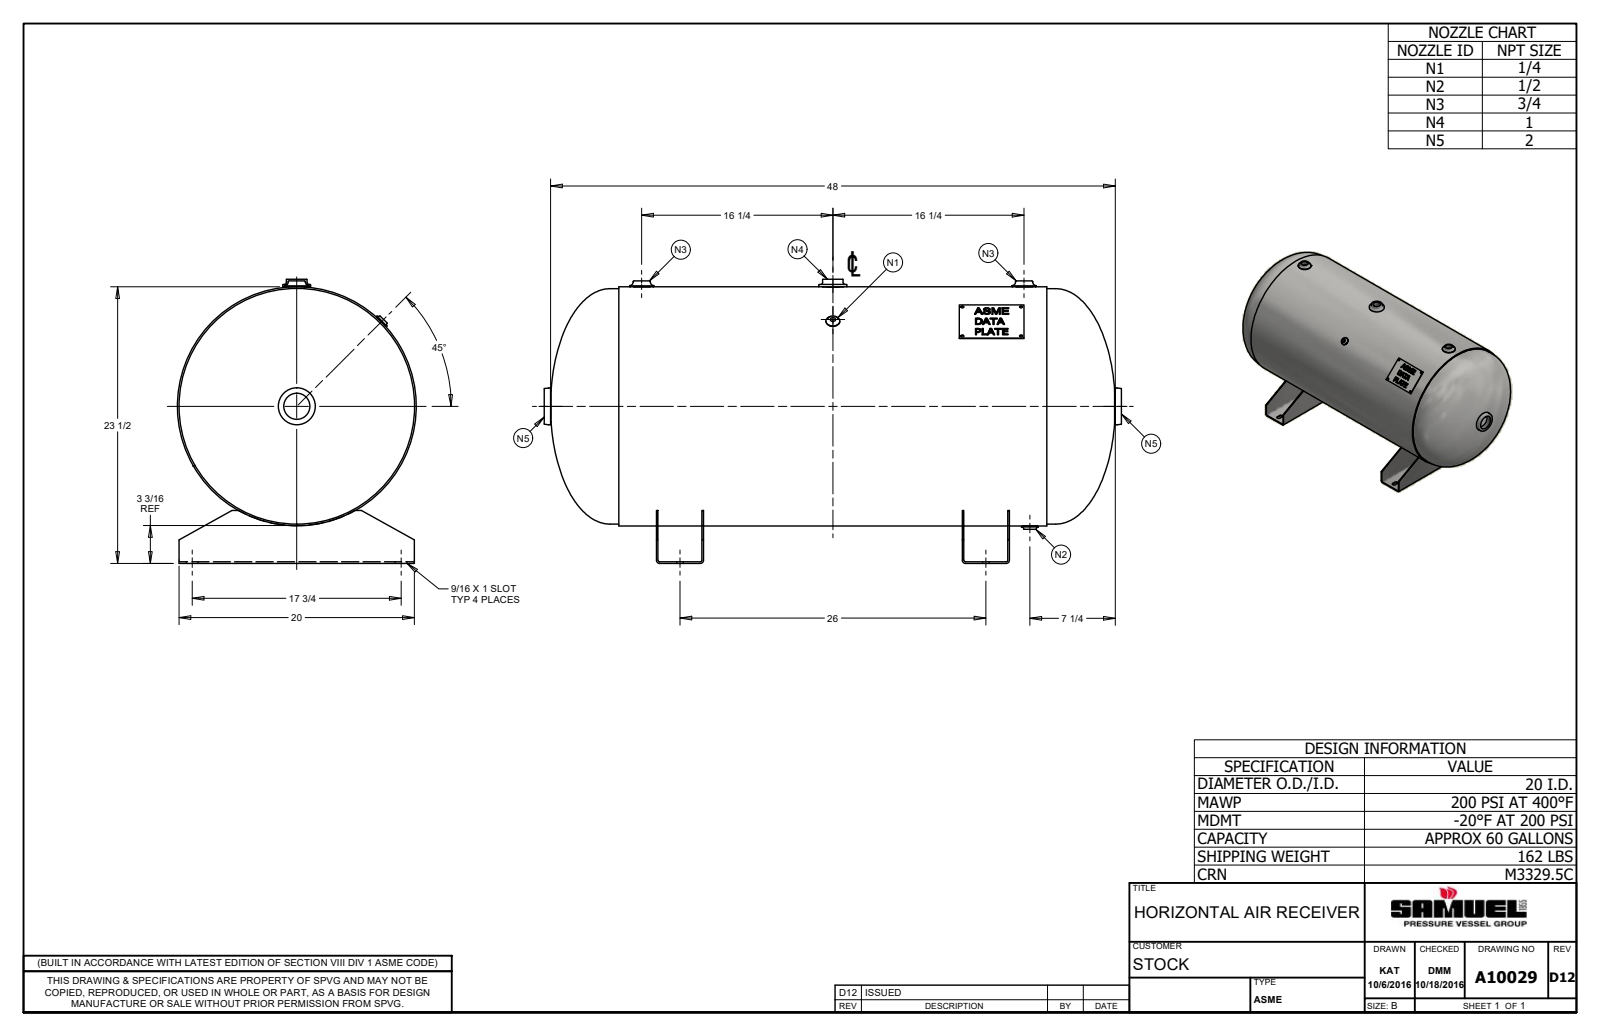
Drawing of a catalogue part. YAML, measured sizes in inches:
part_name: "A10029; A10029-1; A10029-2; 910-800 (+8 more)"
step_written_by: "Autodesk Inventor 2019 (CONFIG_CONTROL_DESIGN)"
units: inches
bodies: {solids: 13, faces: 340, planar: 210, cylindrical: 52, other: 78}
overall_size: [49.063, 24.136, 20.312]
volume: 540.1
surface_area: 7507
round_holes:
  - {diameter: 0.25, count: 4}
  - {diameter: 1.437, count: 2}
  - {diameter: 0.451, count: 1}
  - {diameter: 0.734, count: 1}
  - {diameter: 1.063, count: 1}
  - {diameter: 1.193, count: 1}
  - {diameter: 1.25, count: 1}
  - {diameter: 1.813, count: 1}
  - {diameter: 2.231, count: 1}
  - {diameter: 2.687, count: 1}
  - {diameter: 19.752, count: 1}
round_bosses_or_shafts:
  - {diameter: 2.063, count: 2}
  - {diameter: 1.453, count: 2}
  - {diameter: 20.312, count: 1}
  - {diameter: 20, count: 1}
  - {diameter: 3.125, count: 1}
  - {diameter: 2.375, count: 1}
  - {diameter: 1.75, count: 1}
  - {diameter: 1.703, count: 1}
partial_cylinders:
  - {radius: 0.281, count: 8}
  - {radius: 0.134, count: 4}
  - {radius: 0.269, count: 4}
  - {radius: 10.062, count: 1}
face_to_face_distances: [0.135, 3.865, 26, 0.134, 29.865, 4, 26.135, 3.731, 25.865, 22.135]
hole_center_spacings: [11.138, 16.095, 3.5, 5, 6.103, 16.25, 0.5, 16.75]
